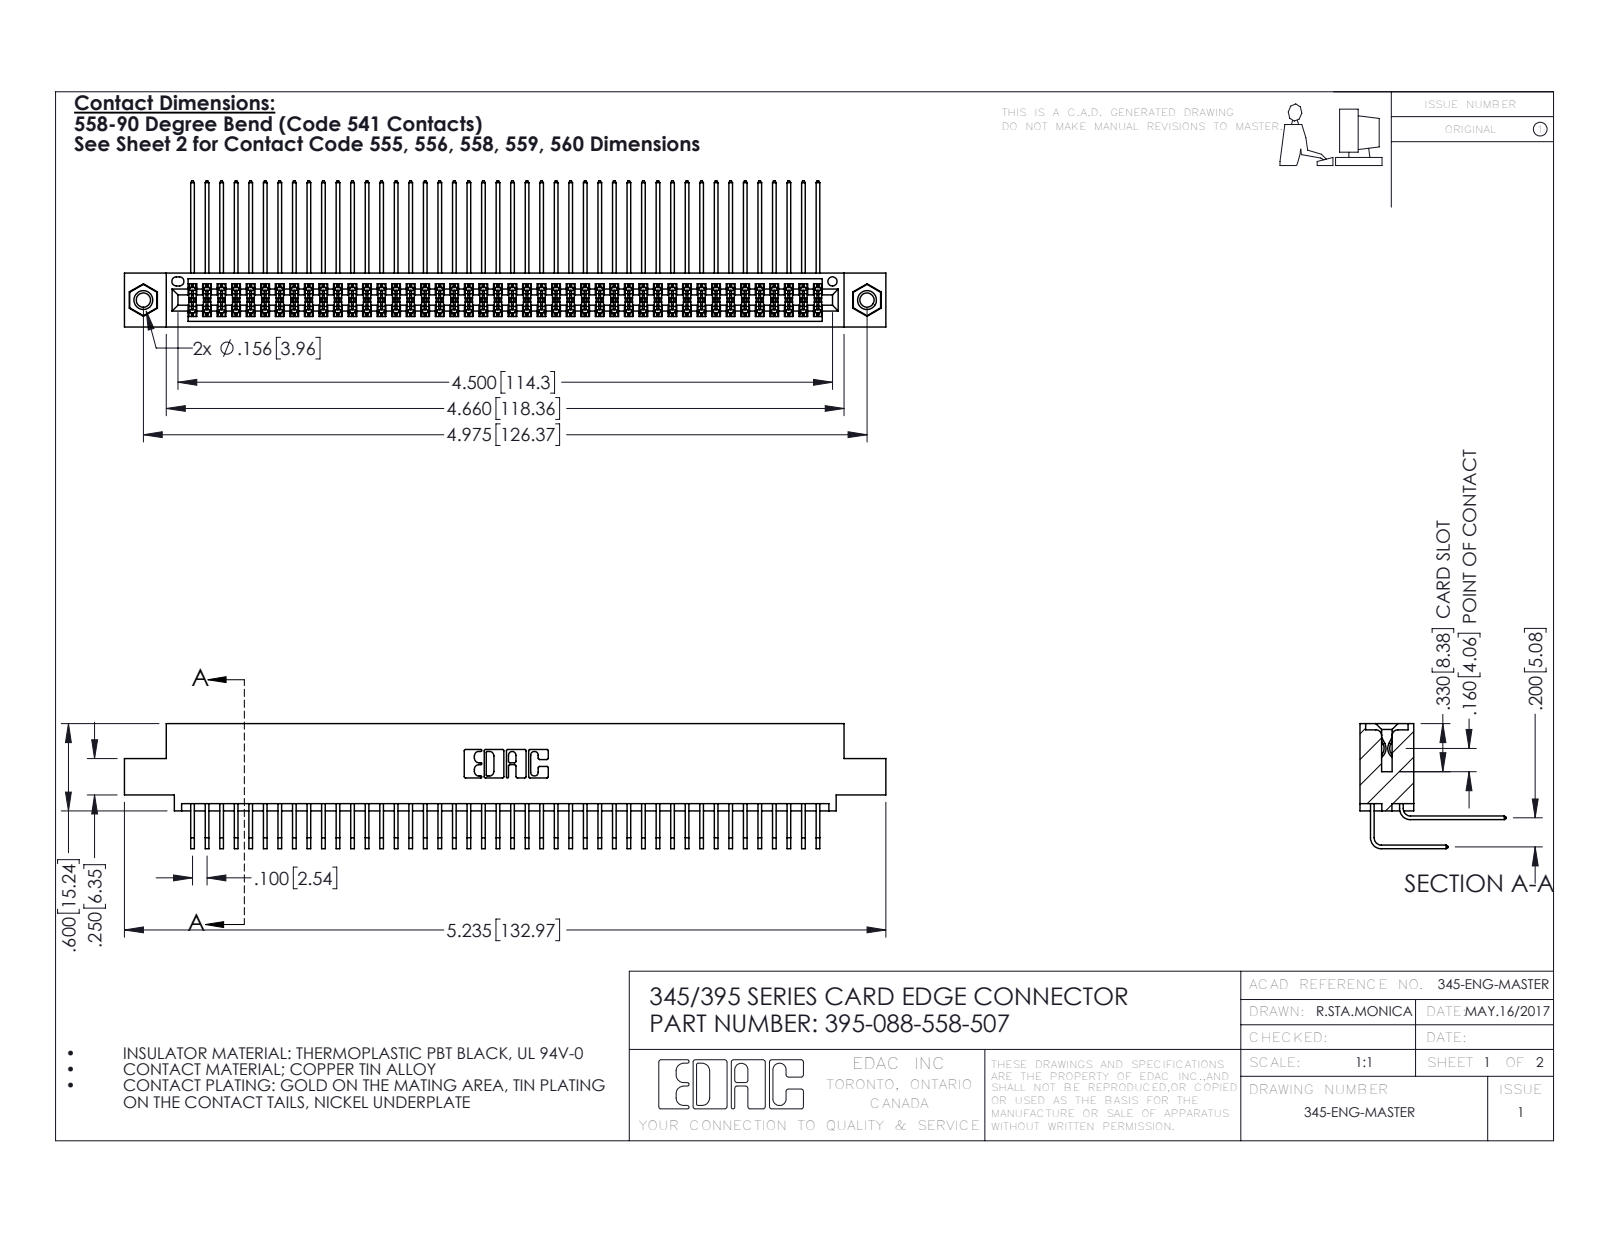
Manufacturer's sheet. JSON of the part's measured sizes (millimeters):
{"part_name": "345-250-001_345-250-005-103; 345 Part_0.110 Offset - 0.156 Dia-TI; 345-292-001_558 Tail - 2; 345-292-001_558 559 Tail - 1 (+1 more)", "step_written_by": "SolidWorks 2016 (CONFIG_CONTROL_DESIGN)", "units": "millimeters", "bodies": {"solids": 91, "faces": 4766, "planar": 3196, "cylindrical": 1554, "other": 16}, "overall_size": [133, 25.5, 21.8], "volume_mm3": 13400, "surface_area_mm2": 22290, "round_holes": [[2.5, 2], [3.2, 2], [4, 2], [1.6, 1]], "round_bosses_or_shafts": [[3.9, 2]], "partial_cylinders_radius": [[0.2, 133], [0.3, 22], [0.2, 6], [0.8, 6], [0.7, 3], [0.4, 2], [0.5, 2], [0.6, 2]], "face_to_face_distances": [1.8, 7.6, 5.1, 9.4, 2.5, 6.9, 0.6, 5.7, 0.6, 4.4], "hole_center_spacings": [6.9, 120.4, 126.4]}
